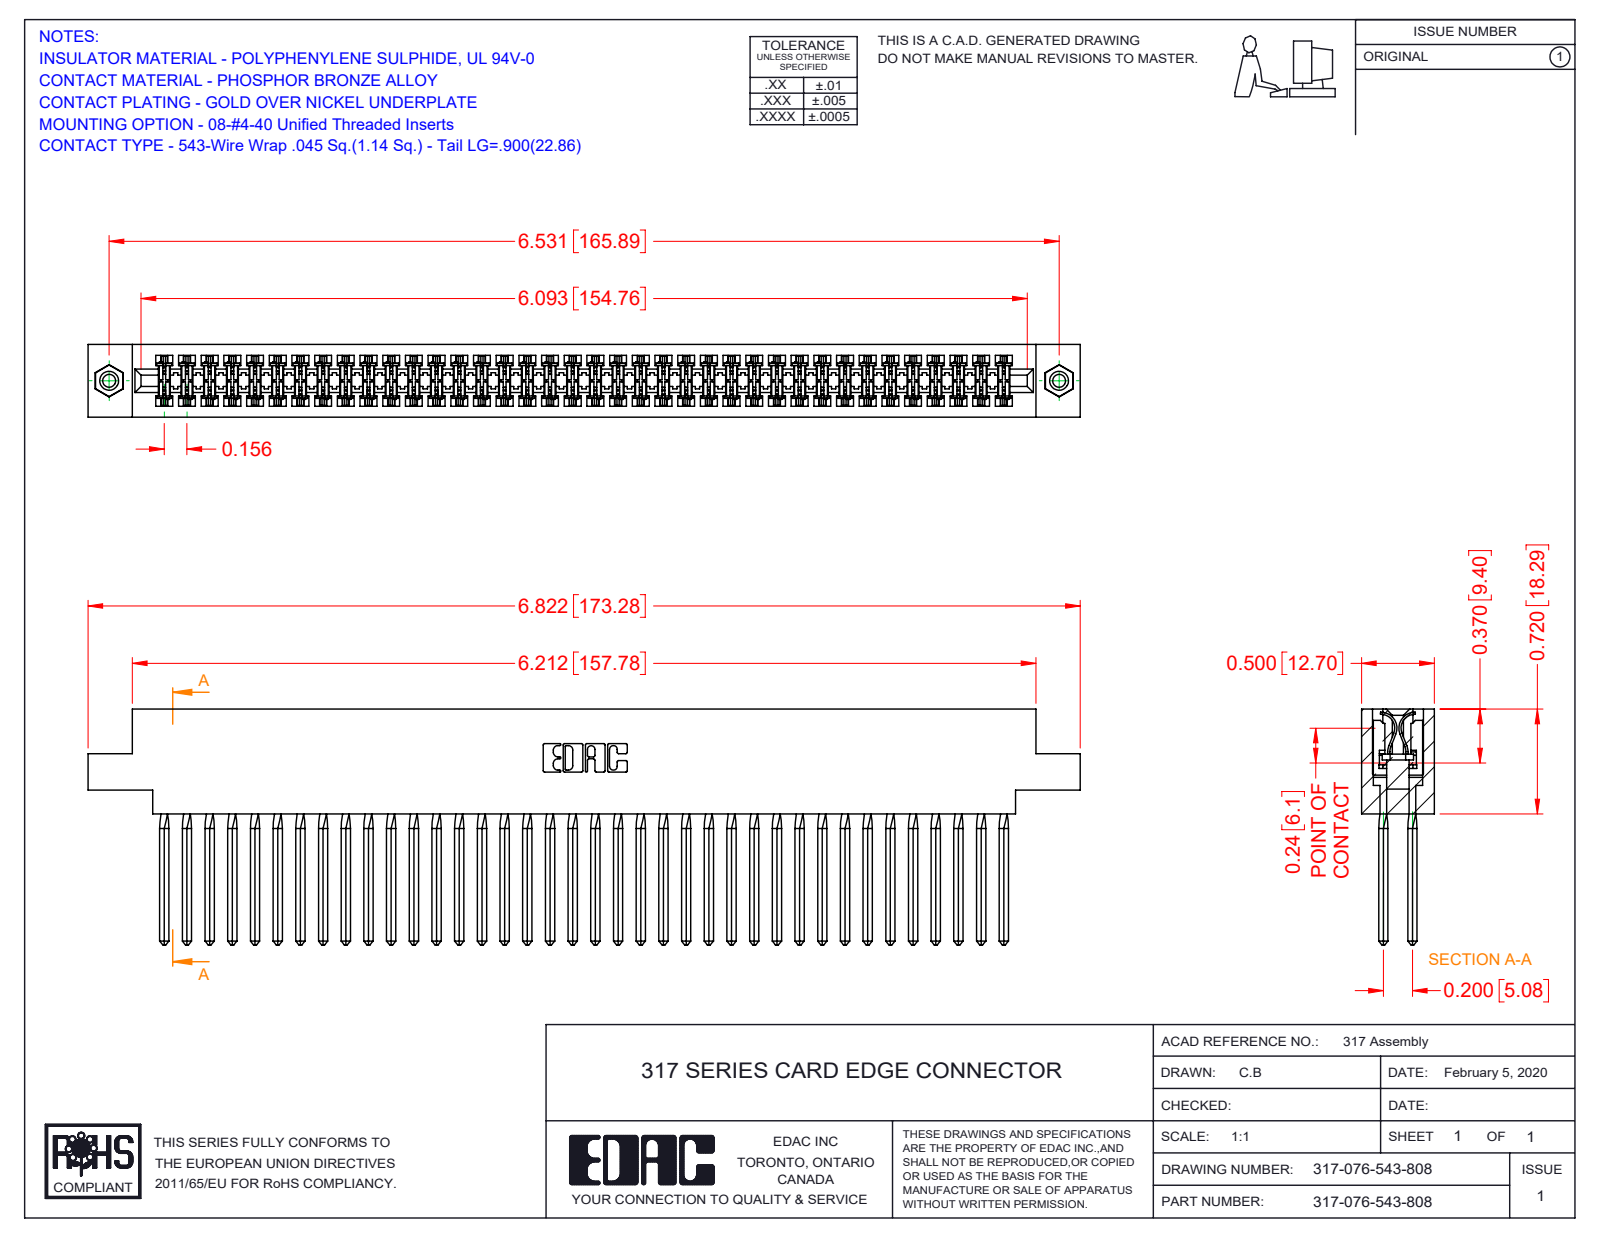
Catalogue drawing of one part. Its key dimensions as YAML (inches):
part_name: "317-290-001_543; 345-250-001_345-250-003-102; 317 Part_.156 Dia - TI; 317-076-543-878"
step_written_by: "SolidWorks 2016 (CONFIG_CONTROL_DESIGN)"
units: inches
bodies: {solids: 79, faces: 6926, planar: 5638, cylindrical: 968, other: 320}
overall_size: [6.822, 1.62, 0.5]
volume: 1.789
surface_area: 68.73
round_holes:
  - {diameter: 0.089, count: 2}
  - {diameter: 0.125, count: 2}
  - {diameter: 0.156, count: 2}
round_bosses_or_shafts:
  - {diameter: 0.155, count: 2}
partial_cylinders:
  - {radius: 0.015, count: 152}
  - {radius: 0.01, count: 22}
  - {radius: 0.007, count: 6}
  - {radius: 0.031, count: 6}
  - {radius: 0.026, count: 3}
  - {radius: 0.095, count: 2}
  - {radius: 0.1, count: 2}
  - {radius: 0.11, count: 2}
face_to_face_distances: [0.5, 0.075, 0.425, 0.35, 0.11, 0.195, 0.094, 0.2, 0.115, 0.131]
hole_center_spacings: [6.531]
